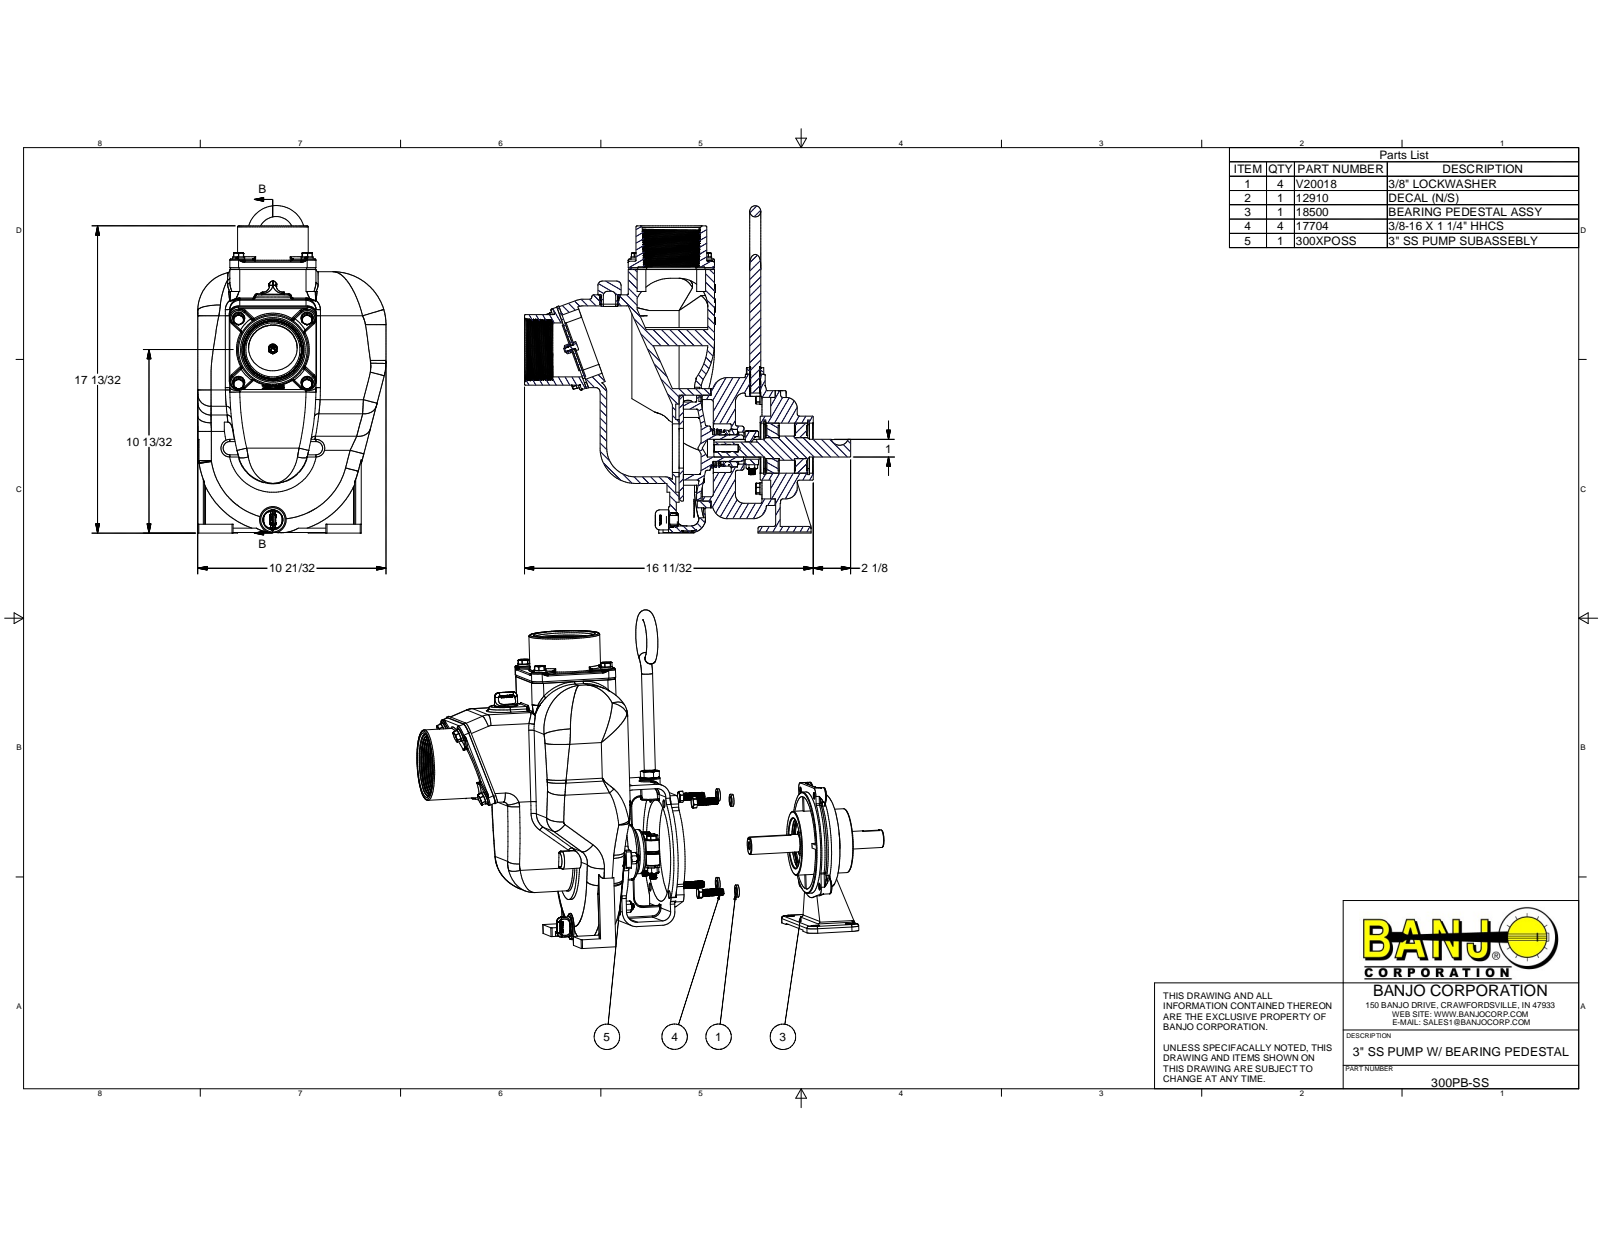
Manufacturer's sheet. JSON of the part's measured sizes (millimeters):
{"part_name": "18001SS; 18004SS; 18106SS; V20018 (+8 more)", "step_written_by": "Autodesk Inventor 2014 (AUTOMOTIVE_DESIGN)", "units": "millimeters", "bodies": {"solids": 79, "faces": 6982, "planar": 1362, "cylindrical": 2405, "other": 3215}, "overall_size": [471.42, 468.75, 270.51], "volume_mm3": 5497000, "surface_area_mm2": 1532000, "round_holes": [[10.32, 22], [7.8, 20], [9.78, 20], [11.11, 10], [7.81, 8], [9.52, 6], [6.35, 4], [11.13, 4], [13.92, 3], [2.79, 2], [7.14, 2], [12.7, 2]], "round_bosses_or_shafts": [[8.24, 272], [17.46, 20], [9.52, 16], [5.39, 12], [9.32, 6], [7.63, 6], [101.6, 2], [171.45, 1]], "partial_cylinders_radius": [[1.52, 95], [3.17, 42], [6.35, 42], [4.12, 32], [12.7, 32], [0.76, 29], [11.11, 24], [25.4, 22]], "face_to_face_distances": [9.52, 9.53, 6.35, 3.18, 55.56, 53.94, 50.8, 4.76, 114.3, 46.04], "hole_center_spacings": [98.42, 139.19, 69.6, 85.72, 98.43, 69.59, 69.58, 69.61]}
